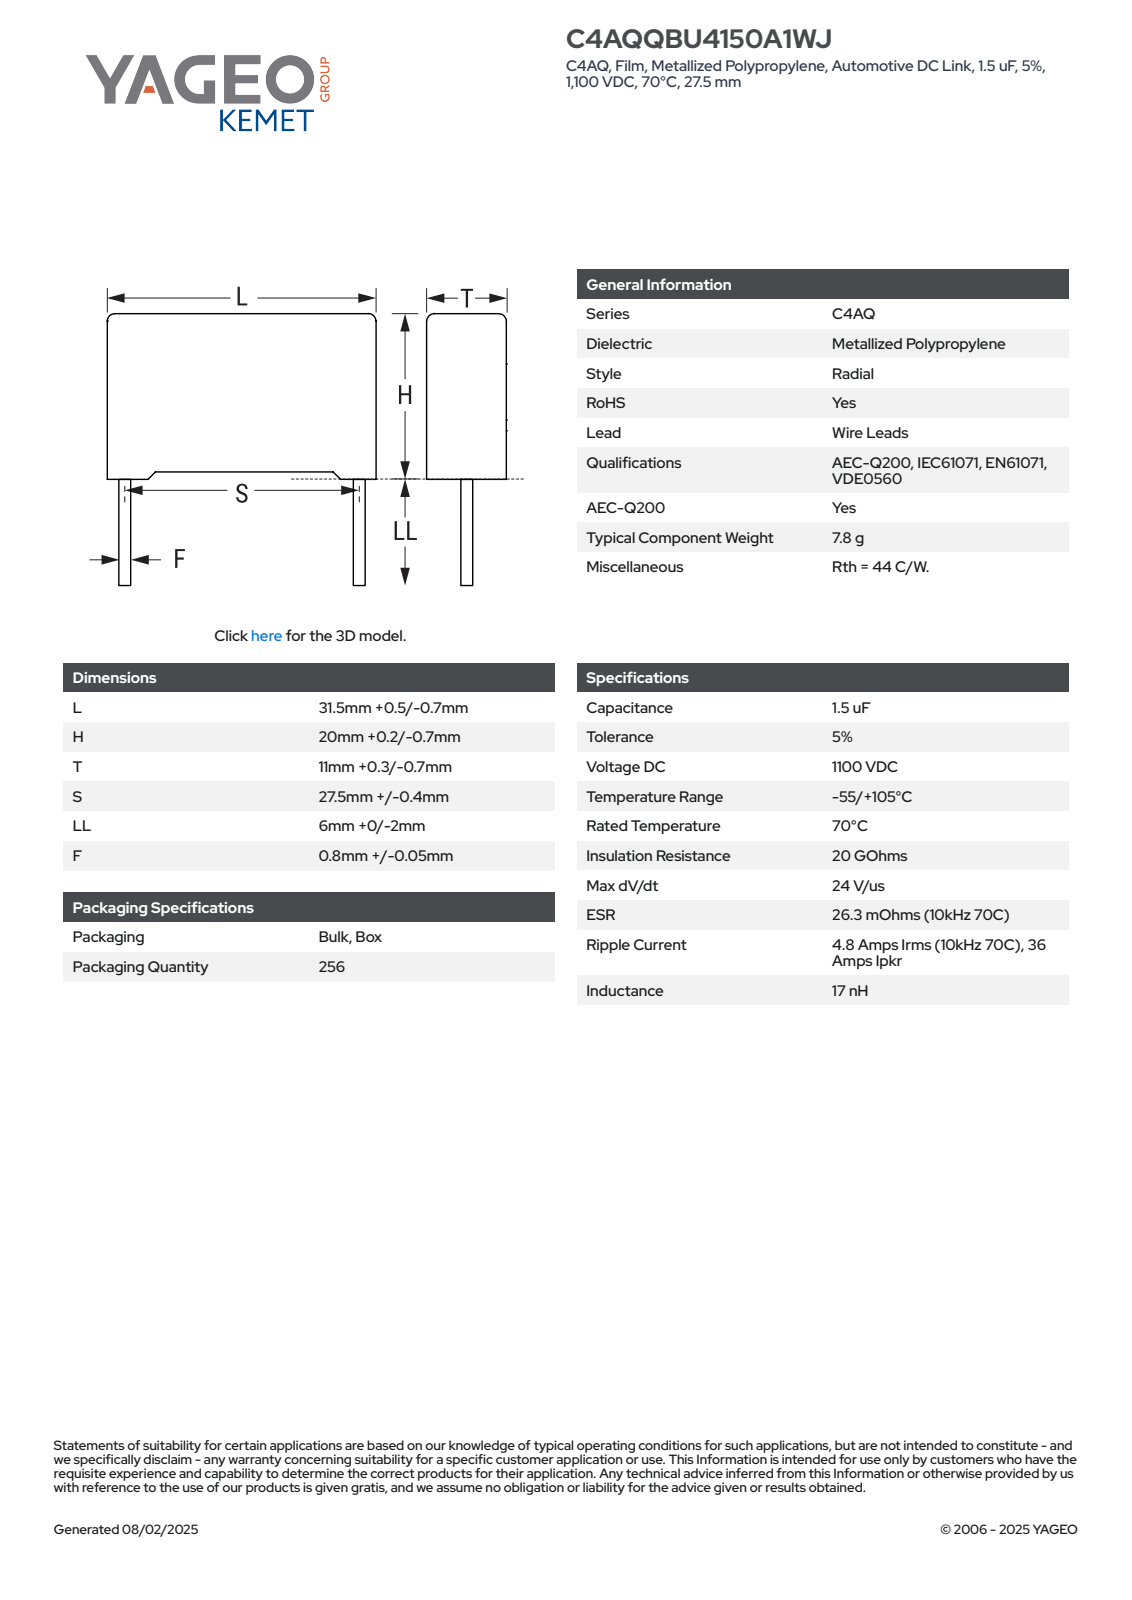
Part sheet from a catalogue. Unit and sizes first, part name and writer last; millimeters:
Units: millimetres
Overall size (bounding box): 32 × 26.2 × 11.3
Round bosses / shafts (diameter × count): ⌀0.85 ×2
Partial cylindrical surfaces — rounded edges, fillets, slot ends (radius × count): R0.5 ×4
Main face-to-face distances: 11.3, 19.45, 32, 19.5, 0.7, 0.75, 20.2, 1.07, 11.31, 30.93
Volume: 7 067 mm³ · Surface area: 2 560 mm²
Bodies: 4 solids, 85 faces (77 planar, 8 cylindrical, 0 other)
Part name (STEP PRODUCT): CFR_RB2CFP_31.5X20X11_L32H20.2T11.3S27.5LL6F0.85
STEP written by: SolidWorks 2014 (AUTOMOTIVE_DESIGN)
